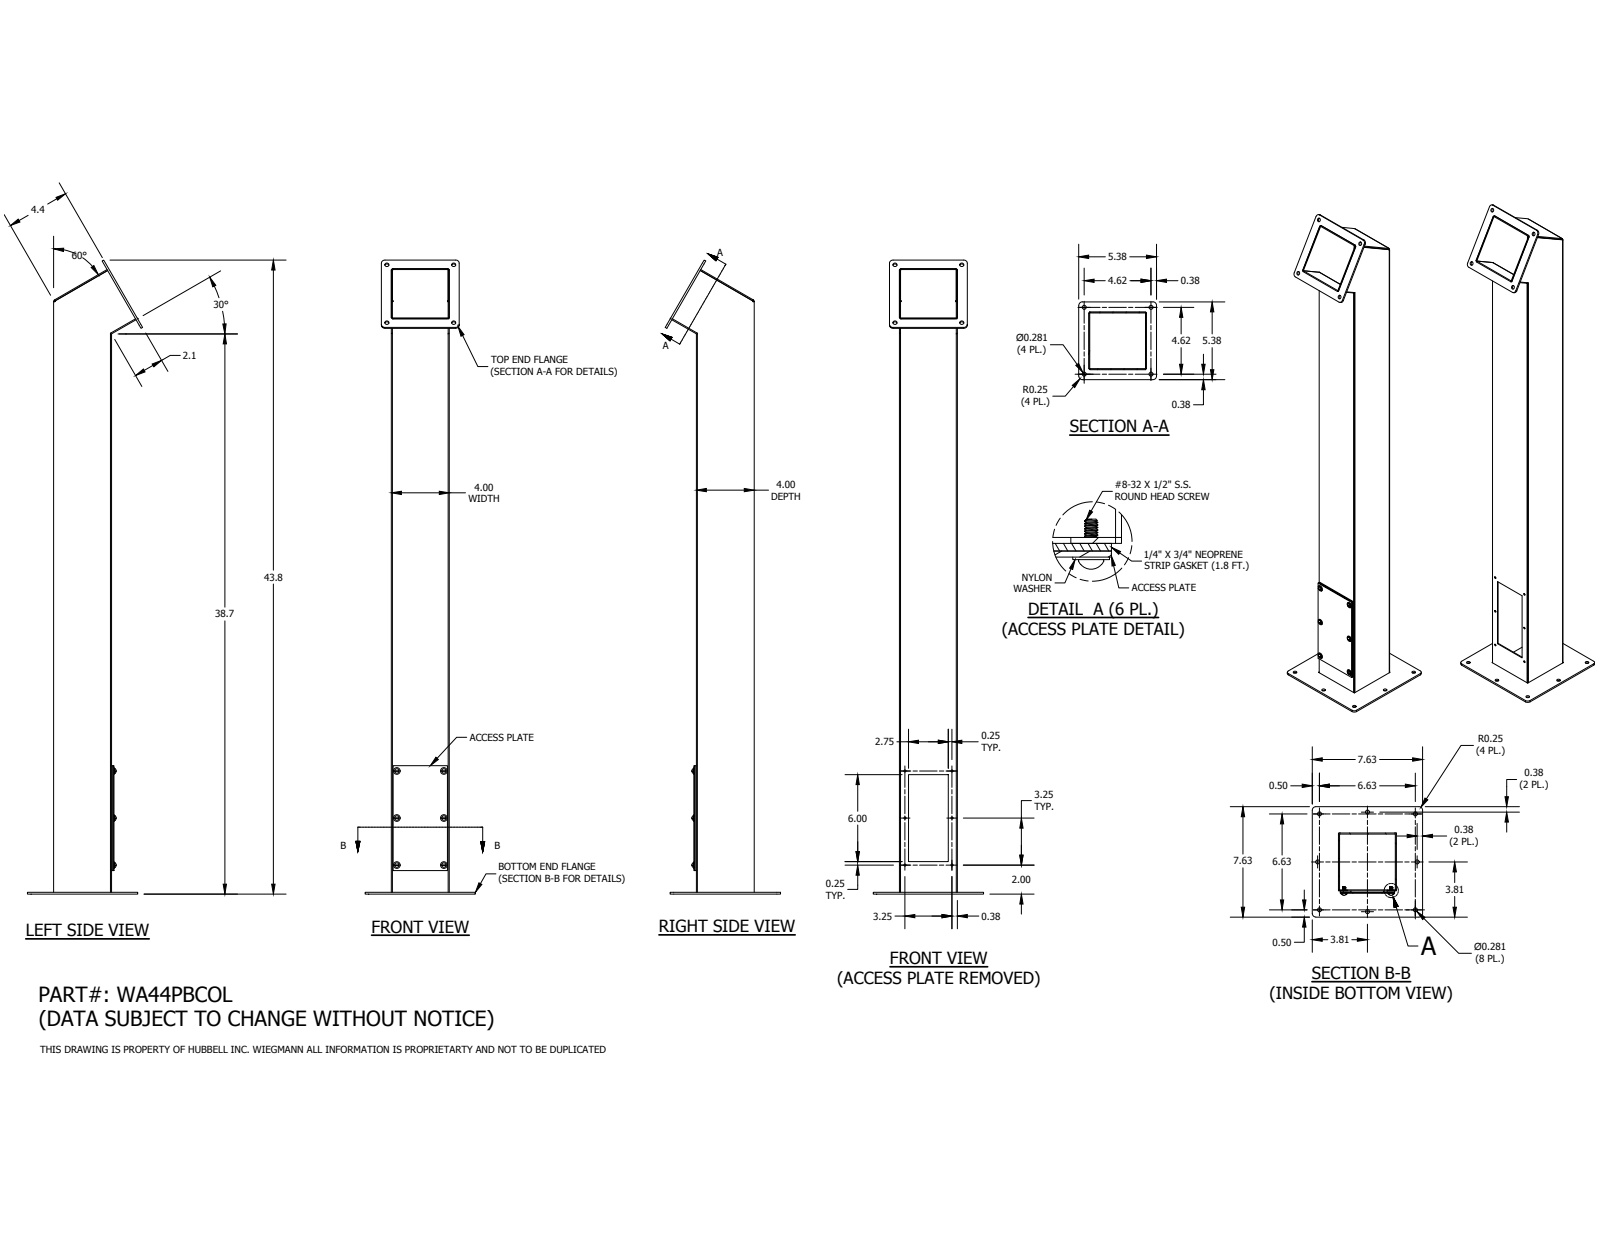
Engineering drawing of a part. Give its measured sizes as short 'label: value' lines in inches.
name: WA44PBCOLFRONT; WA44PBCOLBLR; WA44CCOLBASERING; WA44CCOLCOVER (+5 more)
written by: Autodesk Inventor 2016 (AUTOMOTIVE_DESIGN)
unit: in
bodies: 24 solids, 346 faces (202 planar, 104 cylindrical, 40 other)
size: 43.791 × 7.959 × 7.625
volume: 58.36 in³; area: 1 532 in²
holes: 12× ⌀0.281, 6× ⌀0.14, 6× ⌀0.25, 6× ⌀0.278
bosses: 6× ⌀0.453, 6× ⌀0.309, 6× ⌀0.164, 6× ⌀0.123
rounds: 8× R0.25, 6× R0.089, 5× R0.07, 4× R0.031, 4× R0.105, 4× R0.125
face distances: 0.074, 3.926, 3.852, 4, 4.094, 0.168, 0.125, 4.02, 0.094, 4.168
hole spacings: 3.25, 3.315, 4.596, 7.519, 6.5, 4.615, 4.861, 6.625
